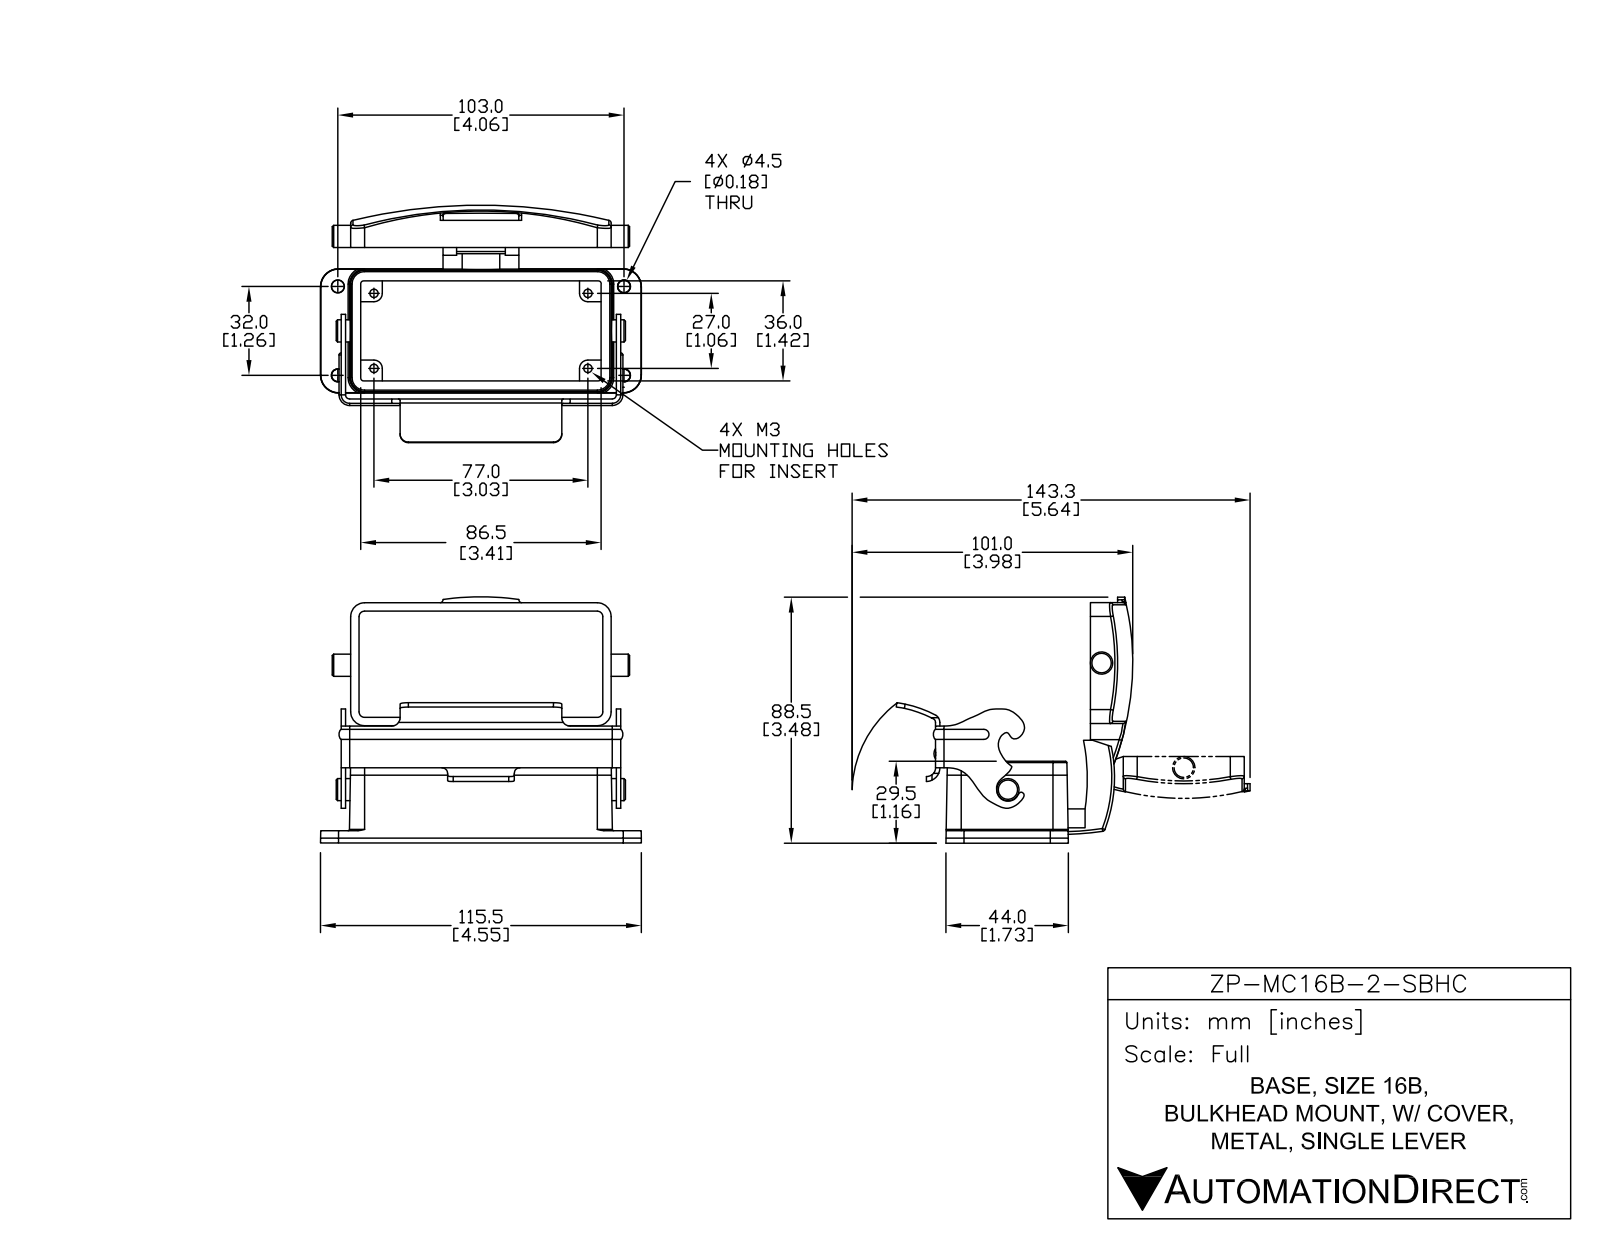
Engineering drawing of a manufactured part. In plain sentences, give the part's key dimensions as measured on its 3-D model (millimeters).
The part is named "ZP-MC16B-2-SBHC". Its 3-D file was written by "SolidWorks 2014 (AUTOMOTIVE_DESIGN)". It is 3 solids with 323 faces: 126 planar, 103 cylindrical and 94 other. Overall it measures 115.7 by 92.11 by 80.31 millimeters. Its volume is 72 258 cubic millimeters and its surface area 45 639 square millimeters. Round holes: 4 of diameter 3, 4 of diameter 4.5, 1 of diameter 2. Round bosses or shafts: 1 of diameter 8, 1 of diameter 7.95. Partial cylindrical surfaces (rounded edges, fillets, slot ends): 10 of radius 0.5, 8 of radius 2, 8 of radius 3, 6 of radius 5, 5 of radius 1, 2 of radius 1.5, 2 of radius 3.06, 2 of radius 8. The main face-to-face distances are 1.56, 3, 36, 40.48, 99.06, 29.45, 35.1, 6.3, 23.15, 37.48. The hole center spacings are 12.99, 32.14, 90.28, 94.95, 27, 32, 77.5, 82.07.
